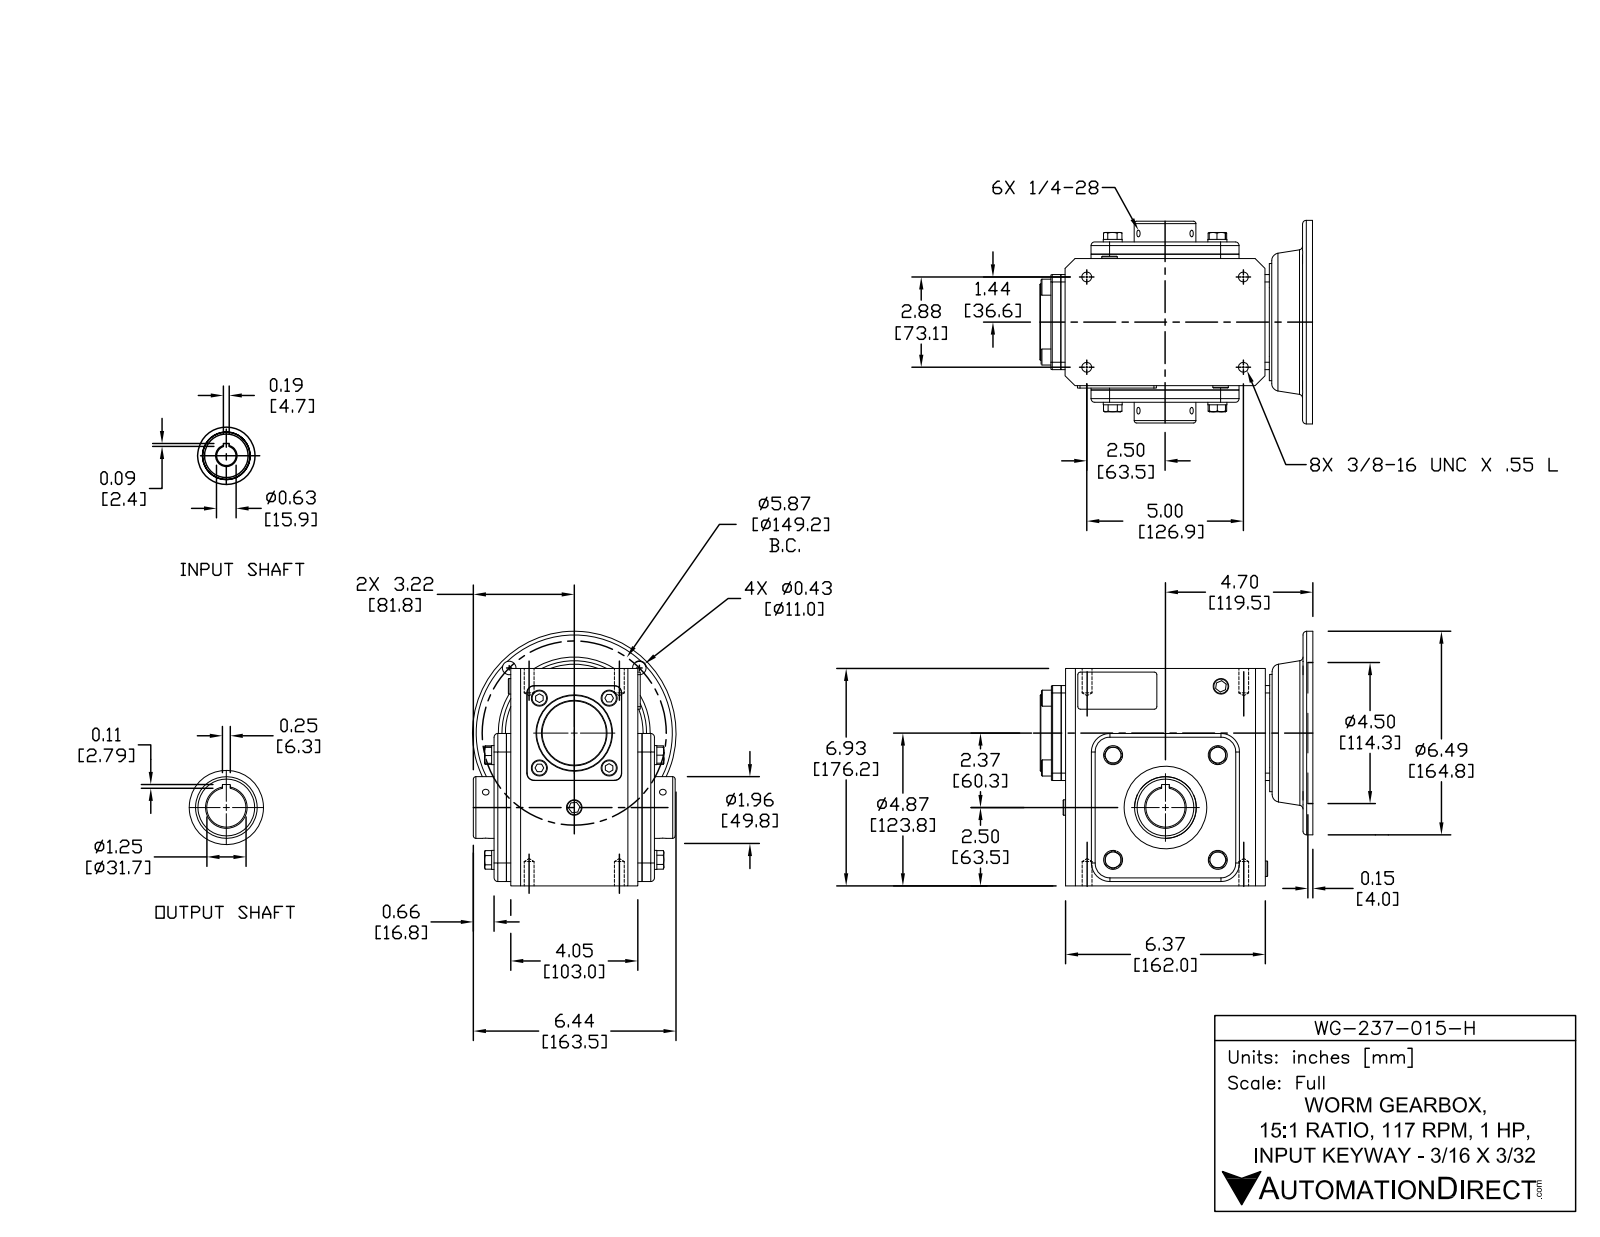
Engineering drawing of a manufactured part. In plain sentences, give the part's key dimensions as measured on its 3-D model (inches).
The part is named "WG-237-015-H". Its 3-D file was written by "SolidWorks 2015 (CONFIG_CONTROL_DESIGN)". It is 37 solids with 609 faces: 348 planar, 172 cylindrical and 89 other. Overall it measures 8.701 by 8.123 by 6.496 inches. Its volume is 217.1 cubic inches and its surface area 540.6 square inches. Round holes: 6 of diameter 0.213, 4 of diameter 0.313, 4 of diameter 0.406, 1 of diameter 0.591, 1 of diameter 0.625, 1 of diameter 1.181, 1 of diameter 1.25, 1 of diameter 1.457, 1 of diameter 1.969, 1 of diameter 2.638, 1 of diameter 3.819, 1 of diameter 4.5. Round bosses or shafts: 4 of diameter 0.606, 4 of diameter 0.512, 1 of diameter 6.496, 1 of diameter 3.74, 1 of diameter 2.441, 1 of diameter 2.047, 1 of diameter 1.142. Partial cylindrical surfaces (rounded edges, fillets, slot ends): 8 of radius 0.079, 8 of radius 0.118, 6 of radius 0.236, 4 of radius 0.591, 2 of radius 0.02, 2 of radius 0.039. The main face-to-face distances are 0.138, 4.331, 4.724, 0.531, 0.394, 4.193, 4.587, 6.516, 0.315, 6.937. The hole center spacings are 2.859, 2.937, 4.945, 5.653, 2.098, 2.88, 4.154, 4.154.
